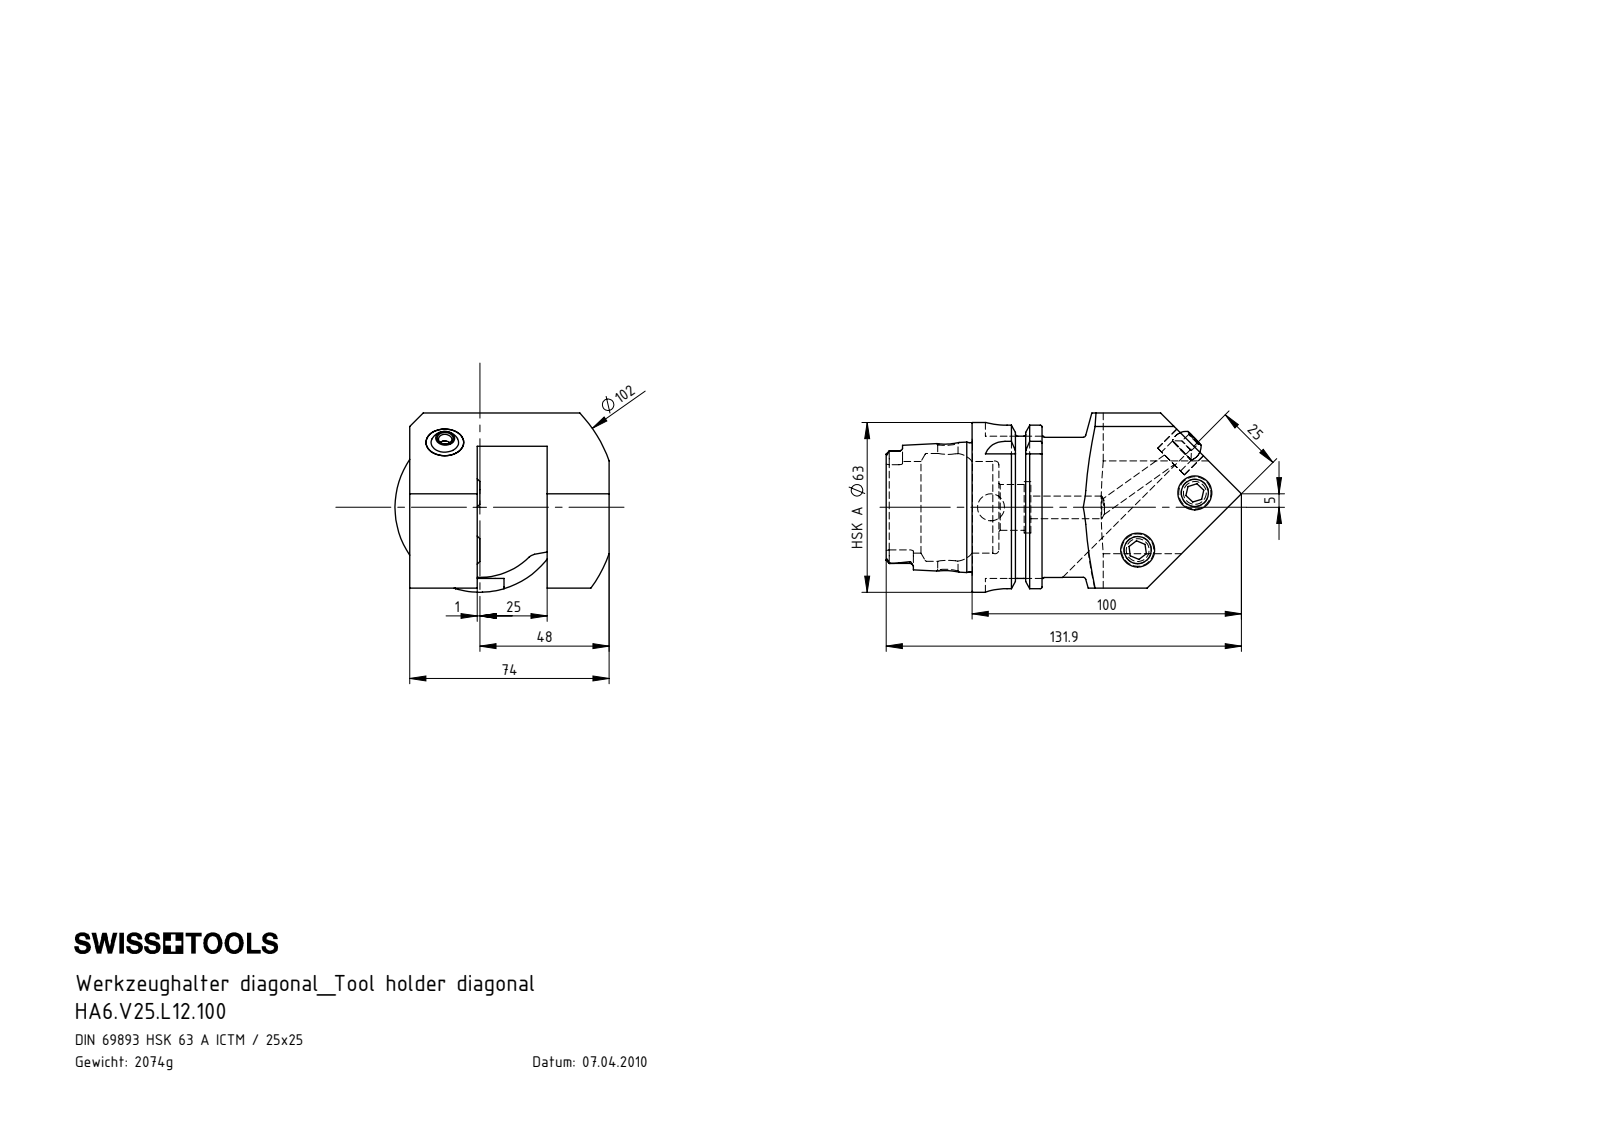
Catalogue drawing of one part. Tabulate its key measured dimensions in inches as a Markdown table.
| quantity | value |
| --- | --- |
| part name | KU1-U14.001.012_1; HA6.V25.L12.100; ISO 4026 - M12 x 25; KU1-U14.001.012_2 (+2 more) |
| STEP written by | SolidWorks 2017 (AUTOMOTIVE_DESIGN) |
| units | inches |
| bodies | 5 solids, 237 faces (80 planar, 65 cylindrical, 92 other) |
| overall size | 5.193 × 3.13 × 2.618 |
| volume | 16.16 in³ |
| surface area | 74.65 in² |
| round holes (diameter × count) | 0.197 × 2, 0.394 × 2, 0.402 × 2, 0.295 × 1, 0.331 × 1, 0.551 × 1, 0.669 × 1, 0.748 × 1, 1.339 × 1, 1.575 × 1 |
| round bosses / shafts (diameter × count) | 0.472 × 2, 2.48 × 1, 2.163 × 1, 2.047 × 1, 1.887 × 1, 0.551 × 1 |
| partial cylindrical surfaces (radius × count) | 0.055 × 6, 0.315 × 4, 0.111 × 2, 0.113 × 2, 2.008 × 1 |
| main face-to-face distances | 0.984, 2.913, 0.906, 2.008, 1.024, 1.929, 2.559, 0.63, 1.022, 0.392 |
| hole center spacings | 1.181, 2.233, 2.987 |
